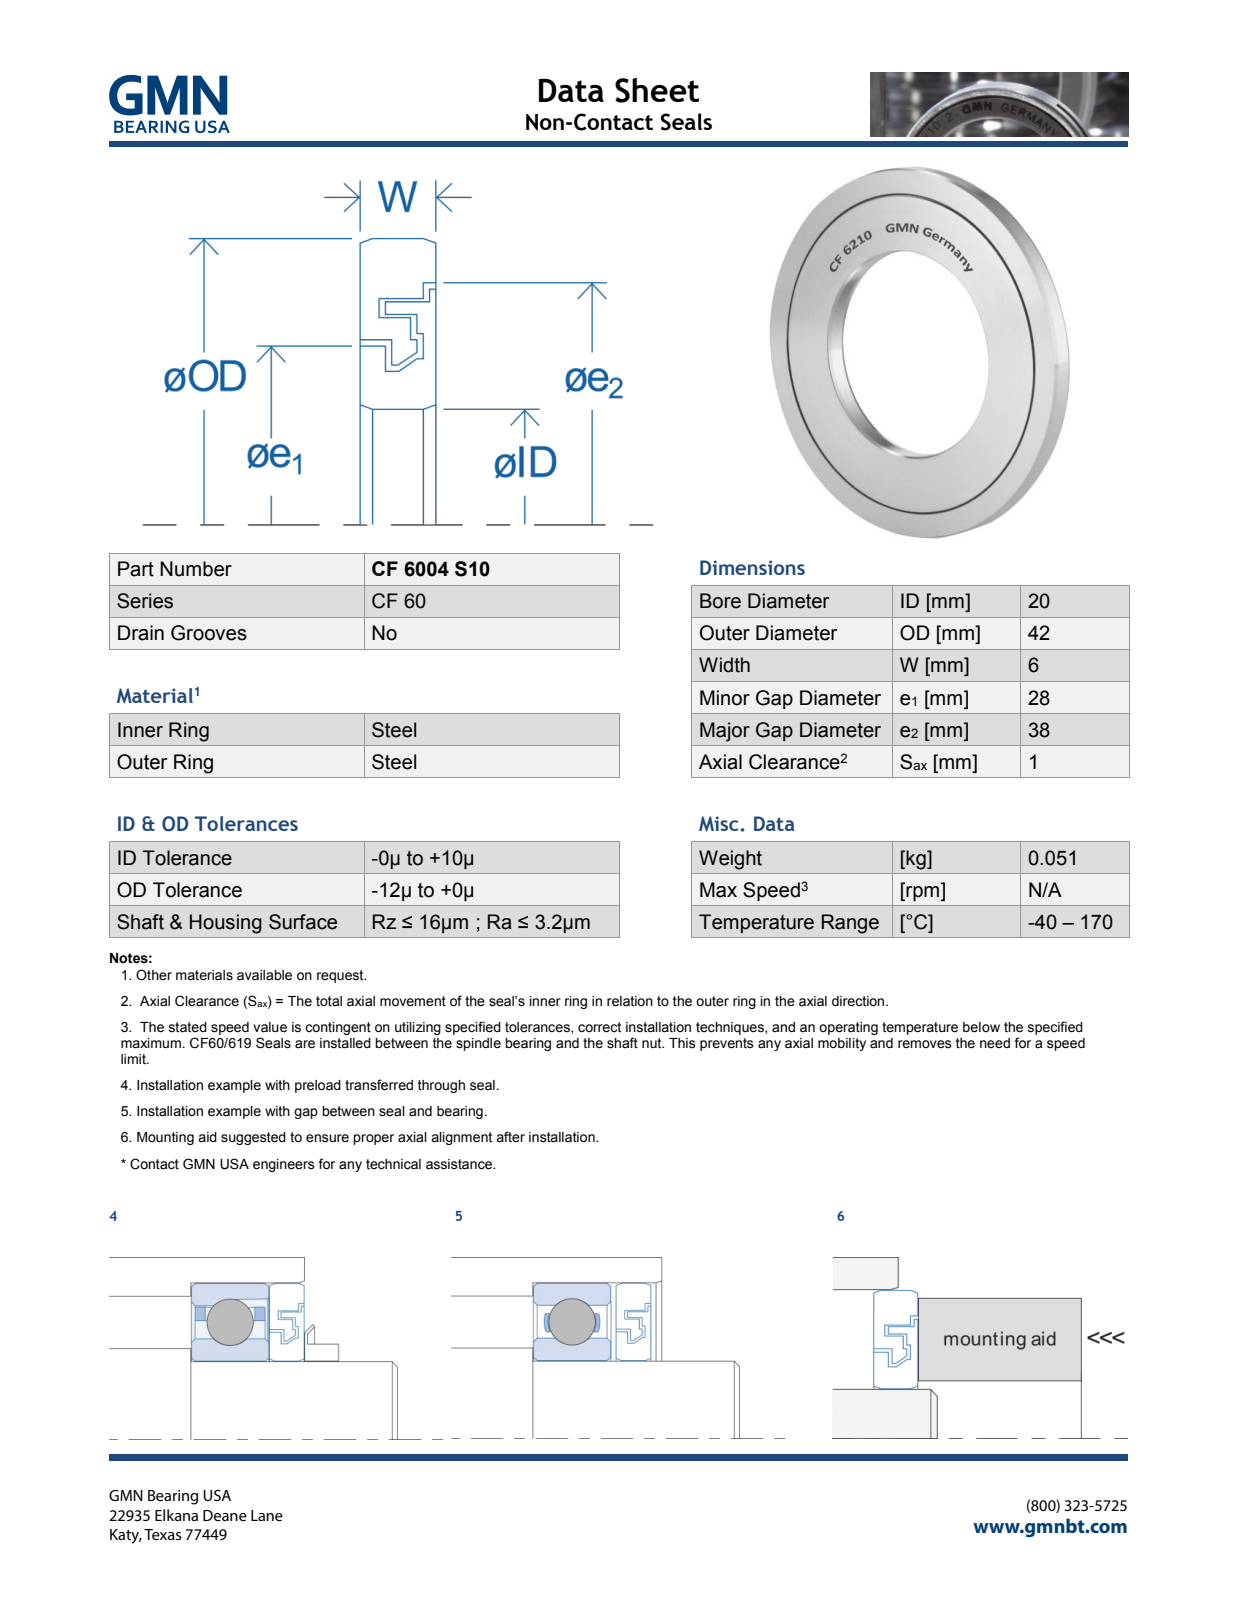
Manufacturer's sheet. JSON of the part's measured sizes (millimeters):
{"part_name": "CF6004S10_PRT", "step_written_by": "PRO/ENGINEER BY PARAMETRIC TECHNOLOGY CORPORATION, 2013150 (AUTOMOTIVE_DESIGN)", "units": "millimeters", "bodies": {"solids": 2, "faces": 661, "planar": 619, "cylindrical": 30, "other": 12}, "overall_size": [42, 42, 6.05], "volume_mm3": 5570, "surface_area_mm2": 6949, "round_holes": [[20, 1], [25, 1], [29, 1], [30, 1], [33, 1], [35.5, 1], [38, 1]], "round_bosses_or_shafts": [[42, 1], [37, 1], [35, 1], [32.5, 1], [28, 1], [26, 1], [24, 1]], "face_to_face_distances": [0.5, 6, 2, 1, 2.5, 1.5, 4, 3, 3.5, 4.5]}
